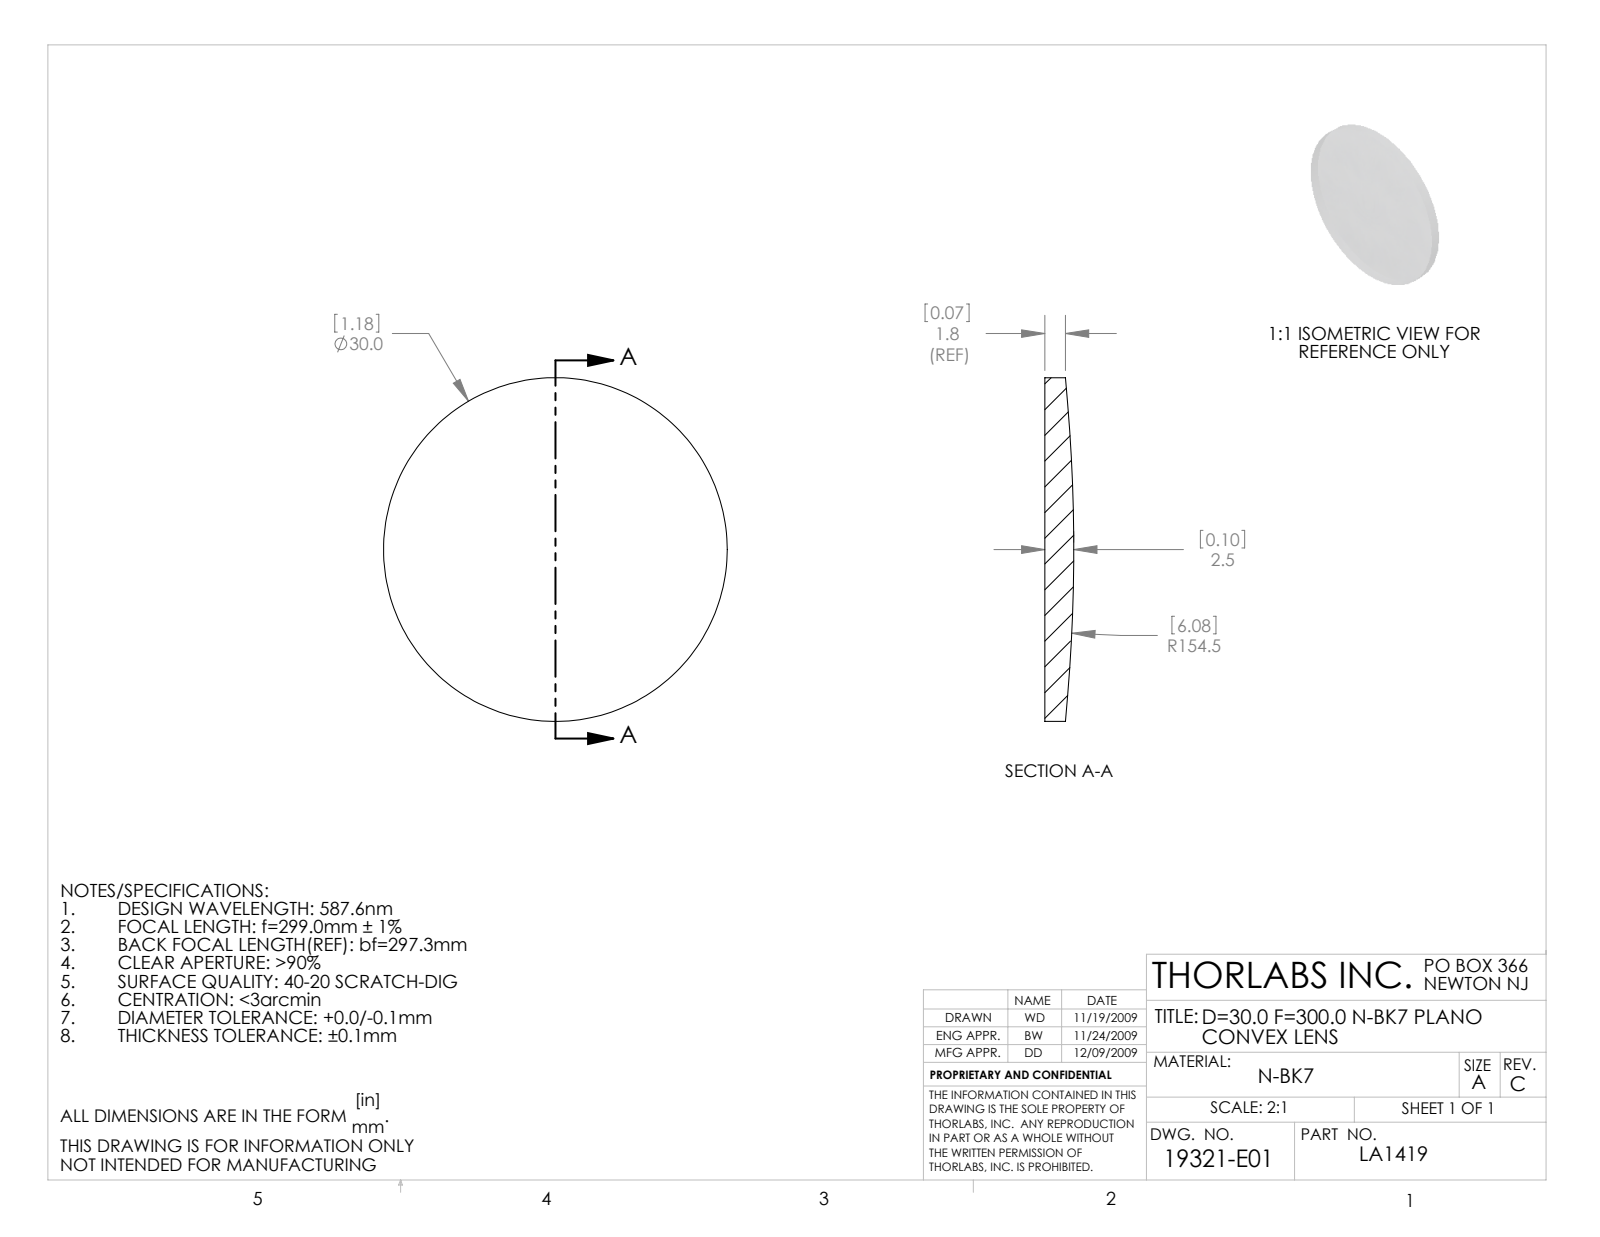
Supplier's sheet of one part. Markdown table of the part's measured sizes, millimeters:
| quantity | value |
| --- | --- |
| part name | 19321-E0W |
| STEP written by | SolidWorks 2009 (AUTOMOTIVE_DESIGN) |
| units | millimeters |
| bodies | 1 solid, 5 faces (1 planar, 2 cylindrical, 2 other) |
| overall size | 30 × 30 × 2.52 |
| volume | 1 524 mm³ |
| surface area | 1 584 mm² |
| round bosses / shafts (diameter × count) | 30 × 1 |
